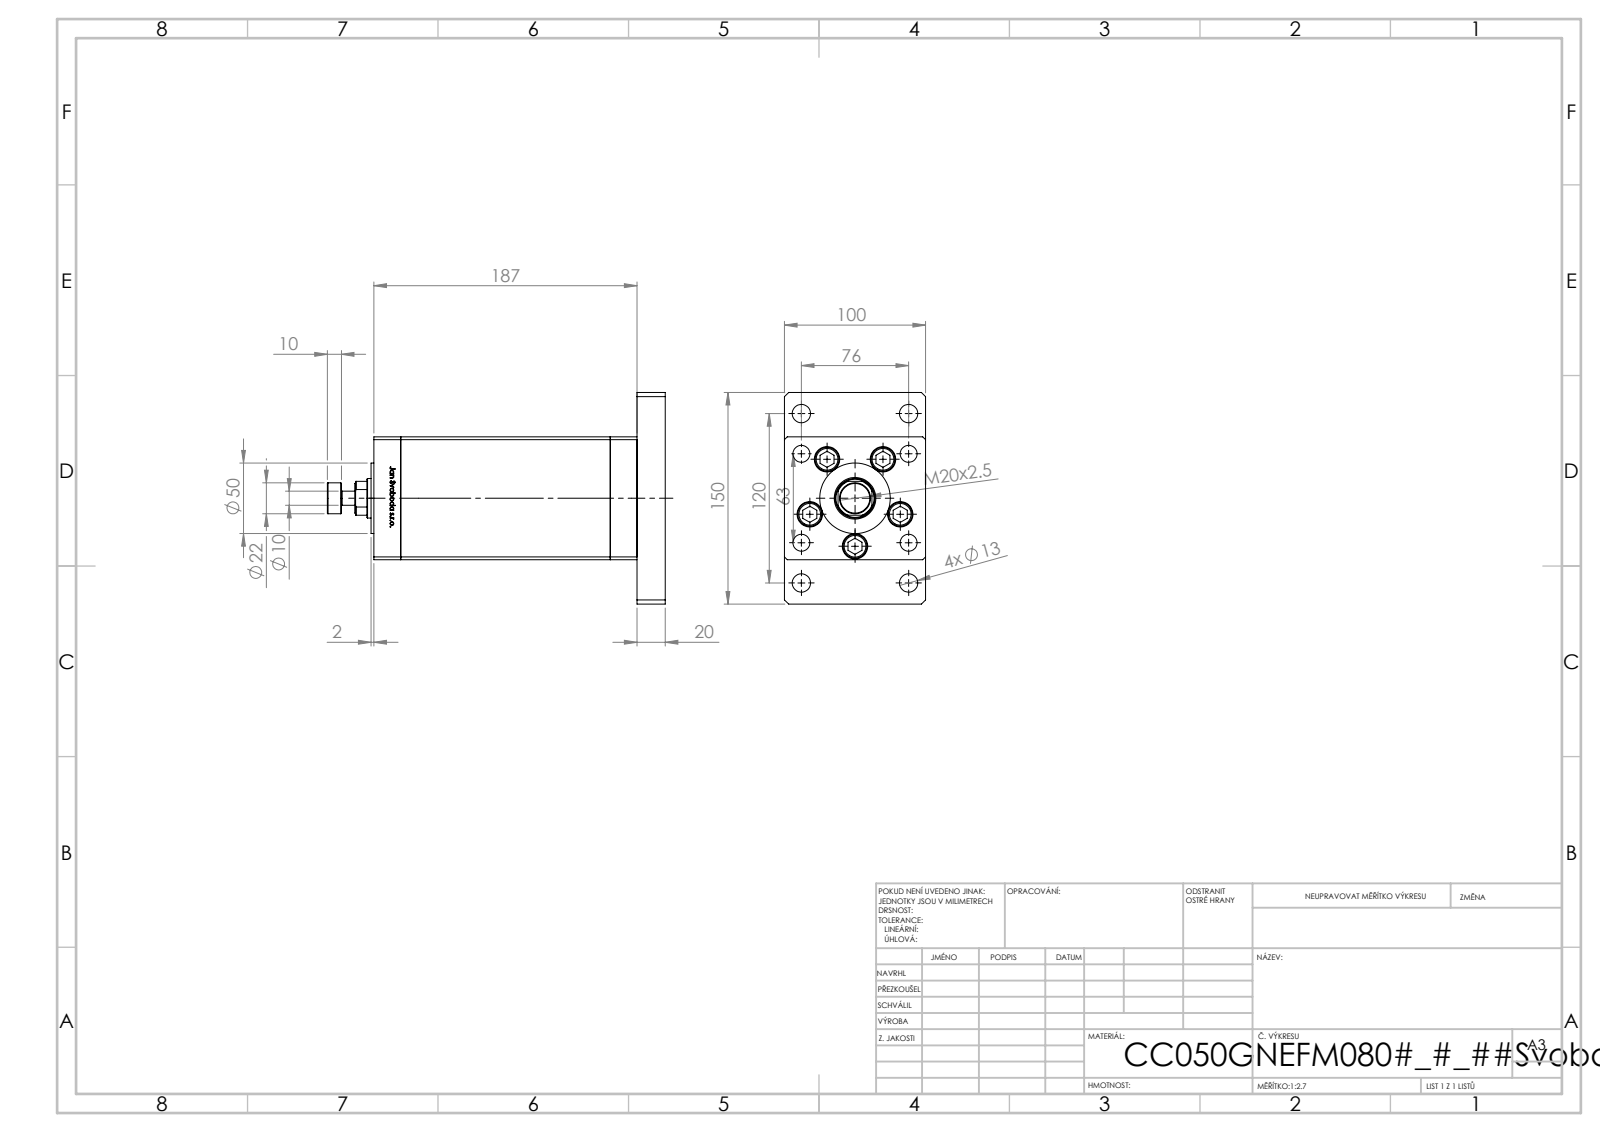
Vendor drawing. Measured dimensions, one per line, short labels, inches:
name: V220C_FRONT_G; ALLEN BOLT; V220CC_FLOATING_JOINT; V220C_G_MIDDLE (+3 more)
written by: SolidWorks 2019 (CONFIG_CONTROL_DESIGN)
unit: in
bodies: 20 solids, 1326 faces (521 planar, 191 cylindrical, 614 other)
size: 9.429 × 5.906 × 3.937
volume: 103.9 in³; area: 401.3 in²
holes: 9× ⌀0.472, 5× ⌀0.531, 5× ⌀0.709, 4× ⌀0.512, 4× ⌀0.669, 2× ⌀0.079, 2× ⌀0.518, 1× ⌀0.728, 1× ⌀1.102, 1× ⌀1.161, 1× ⌀2.677
bosses: 9× ⌀0.315, 5× ⌀0.669, 1× ⌀1.969, 1× ⌀0.866, 1× ⌀0.394
rounds: 2× R0.037, 1× R0.531
face distances: 0.748, 3.937, 6.594, 3.425, 5.846, 0.787, 7.382, 1.535, 8.13, 7.343
hole spacings: 1.339, 1.122, 1.943, 2.796, 2.992, 3.196, 3.602, 4.683
